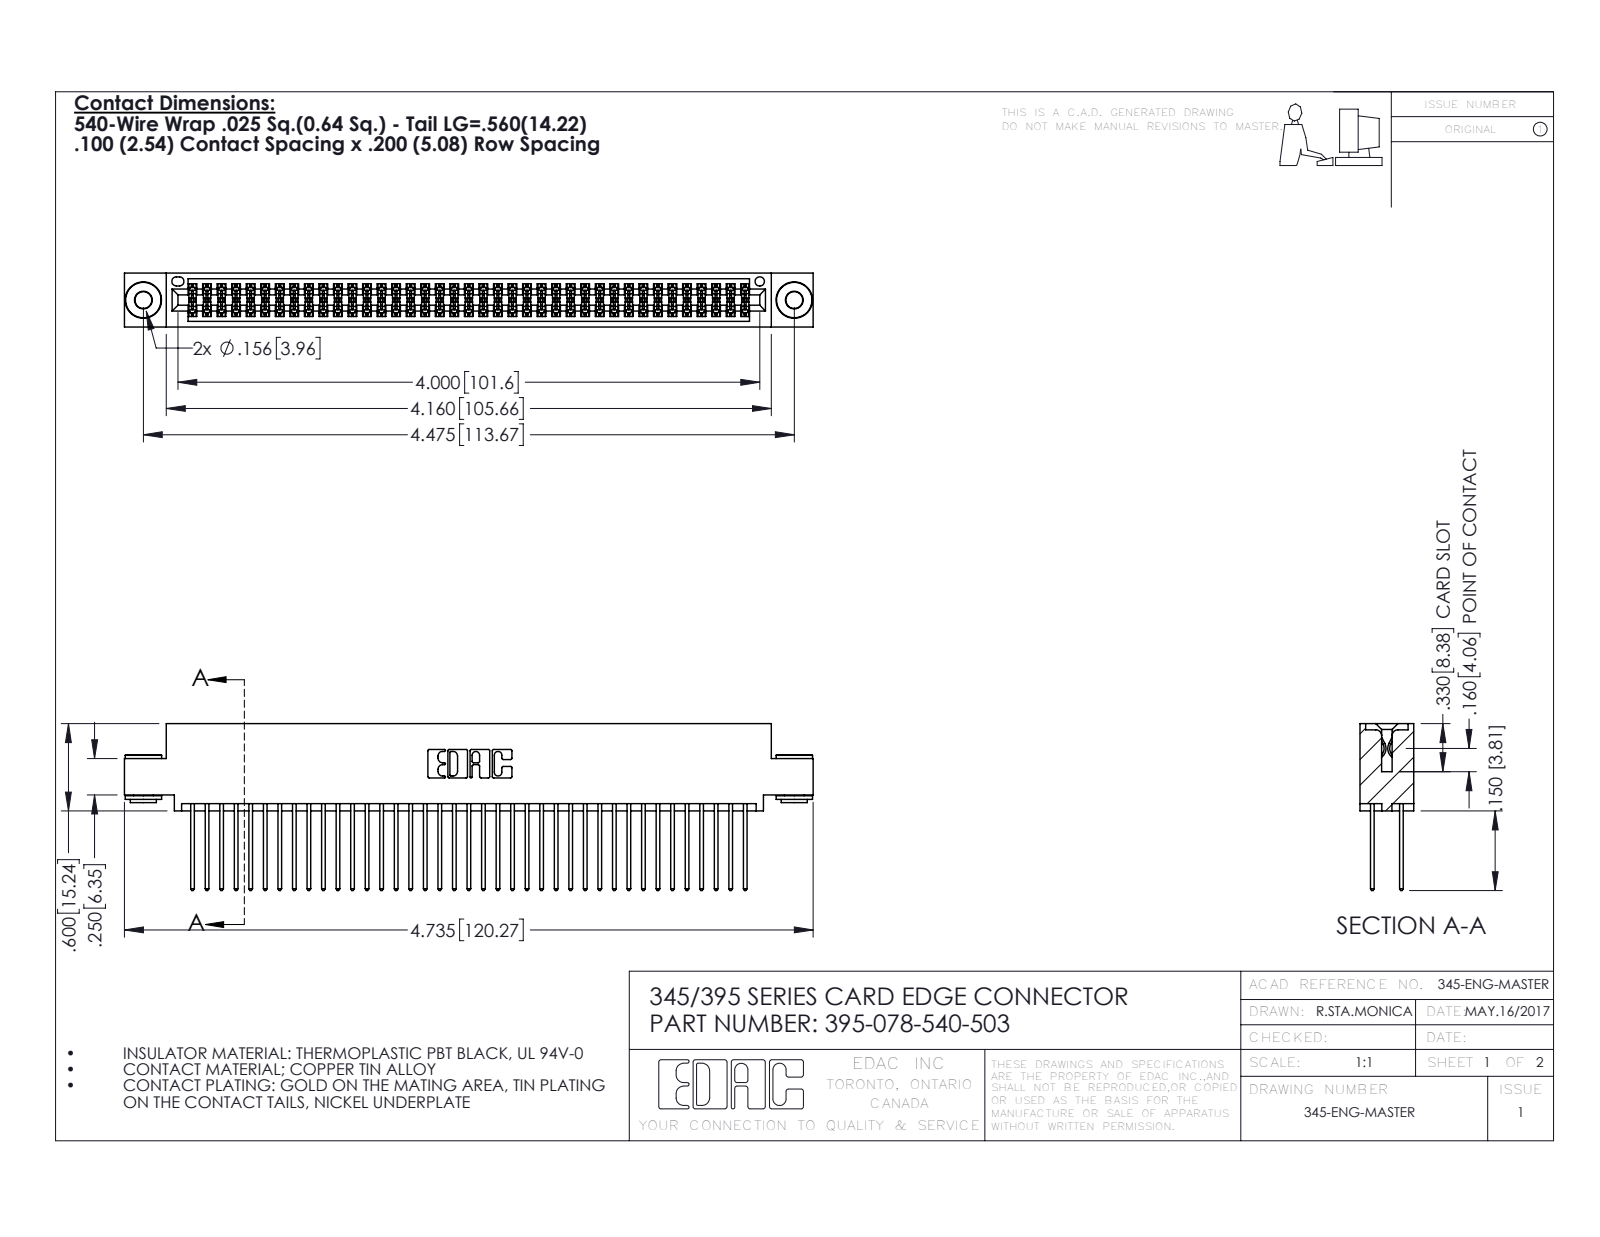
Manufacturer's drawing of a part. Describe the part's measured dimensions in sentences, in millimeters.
The part is named "395-078-540-503; 345-250-002_345-250-002-102; 345-292-001_345-293-140; 345 Part_0.110 Offset - 0.156 Dia-TH". Its 3-D file was written by "SolidWorks 2016 (CONFIG_CONTROL_DESIGN)". It is 81 solids with 4068 faces: 2668 planar, 1392 cylindrical and 8 other. Overall it measures 120.3 by 29.1 by 9.4 millimeters. Its volume is 11 900 cubic millimeters and its surface area 19 200 square millimeters. Round holes: 2 of diameter 2.9, 2 of diameter 4, 1 of diameter 1.6. Round bosses or shafts: 2 of diameter 6.4, 2 of diameter 4.6, 2 of diameter 3.5. Partial cylindrical surfaces (rounded edges, fillets, slot ends): 117 of radius 0.2, 78 of radius 0.3, 22 of radius 0.3, 6 of radius 0.2, 6 of radius 0.8, 3 of radius 0.7, 2 of radius 0.4, 2 of radius 0.5. The main face-to-face distances are 1.8, 7.6, 5.1, 0.6, 2.5, 6.9, 9.4, 5.7, 4.4, 3.8. The hole center spacings are 6.9, 107.7, 113.7.
